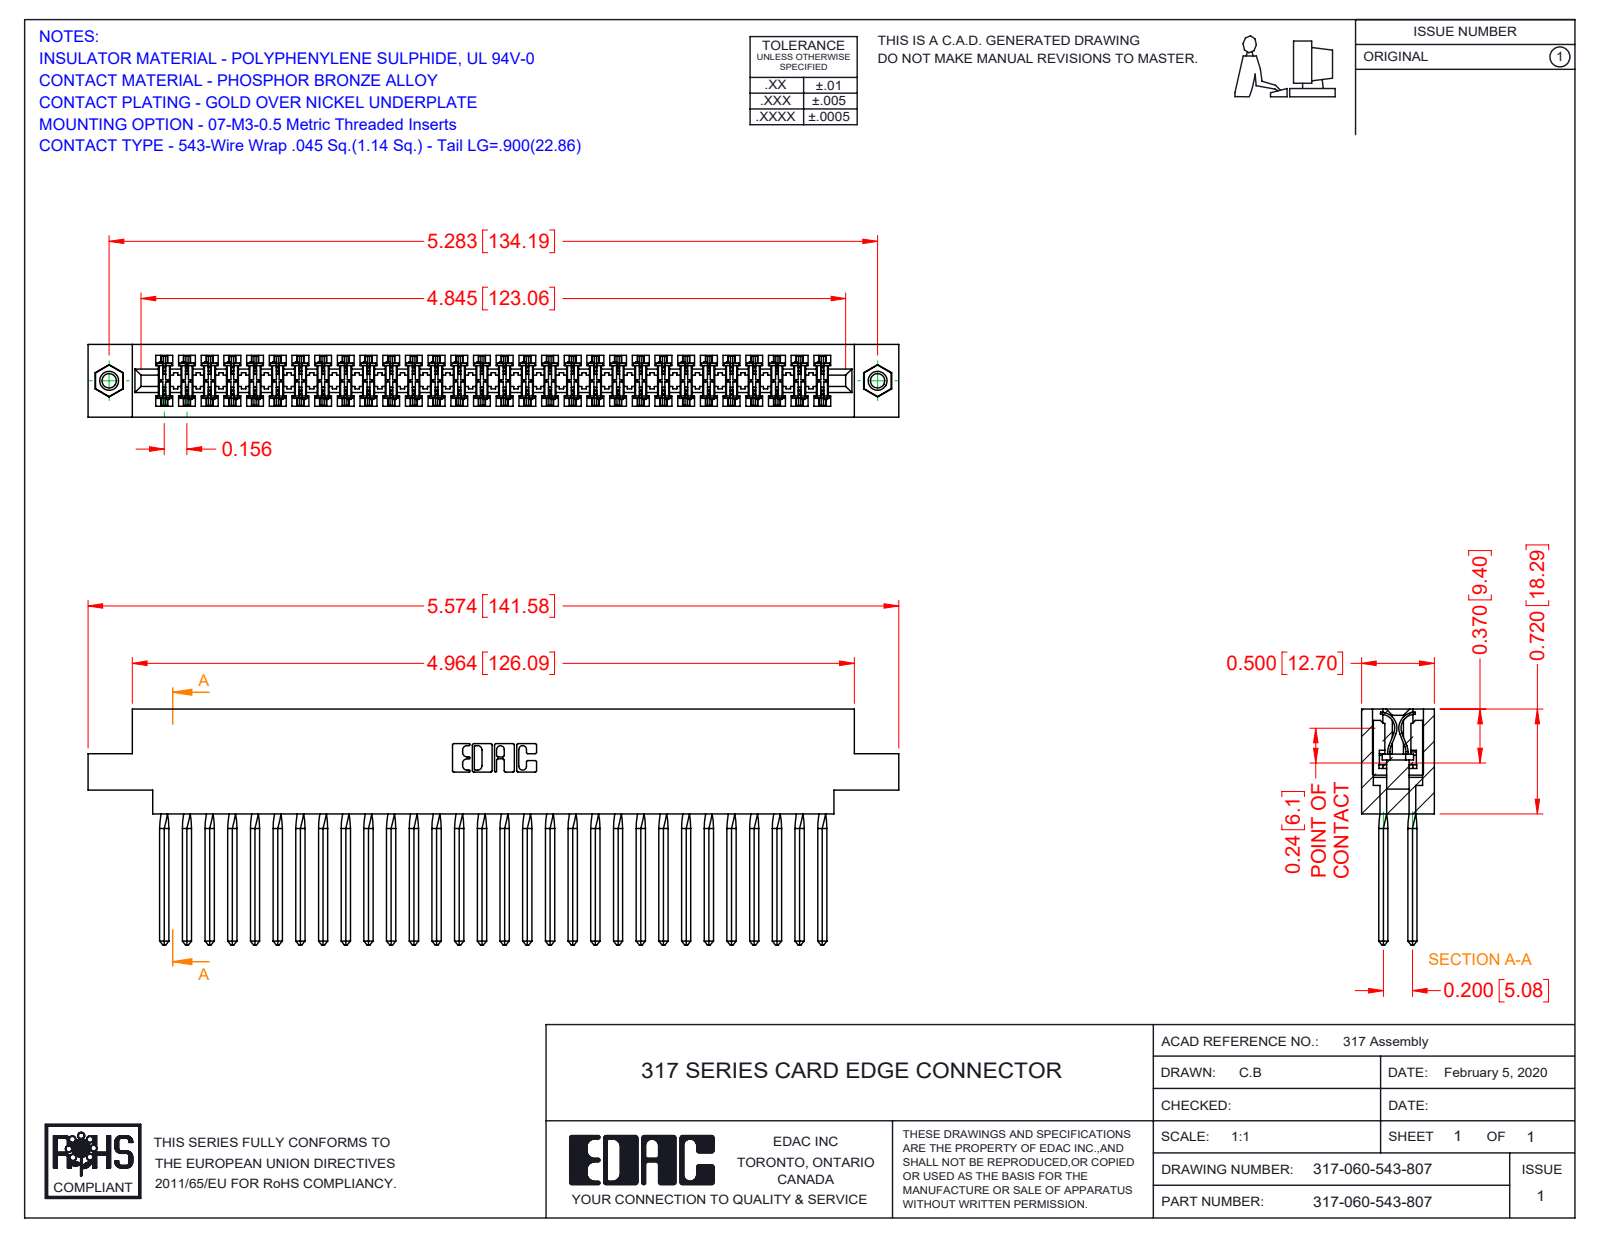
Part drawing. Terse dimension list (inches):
name: 317-290-001_543; 317 Part_.156 Dia - TI; 345-250-001_345-250-005-103; 317-060-543-807
written by: SolidWorks 2016 (CONFIG_CONTROL_DESIGN)
unit: in
bodies: 63 solids, 5502 faces (4470 planar, 776 cylindrical, 256 other)
size: 5.574 × 1.62 × 0.5
volume: 1.443 in³; area: 54.92 in²
holes: 2× ⌀0.098, 2× ⌀0.125, 2× ⌀0.156
bosses: 2× ⌀0.155
rounds: 120× R0.015, 22× R0.01, 6× R0.007, 6× R0.031, 3× R0.026, 2× R0.095, 2× R0.1, 2× R0.11
face distances: 0.5, 0.075, 0.425, 0.35, 0.11, 0.195, 0.094, 0.2, 0.72, 0.115
hole spacings: 5.283
